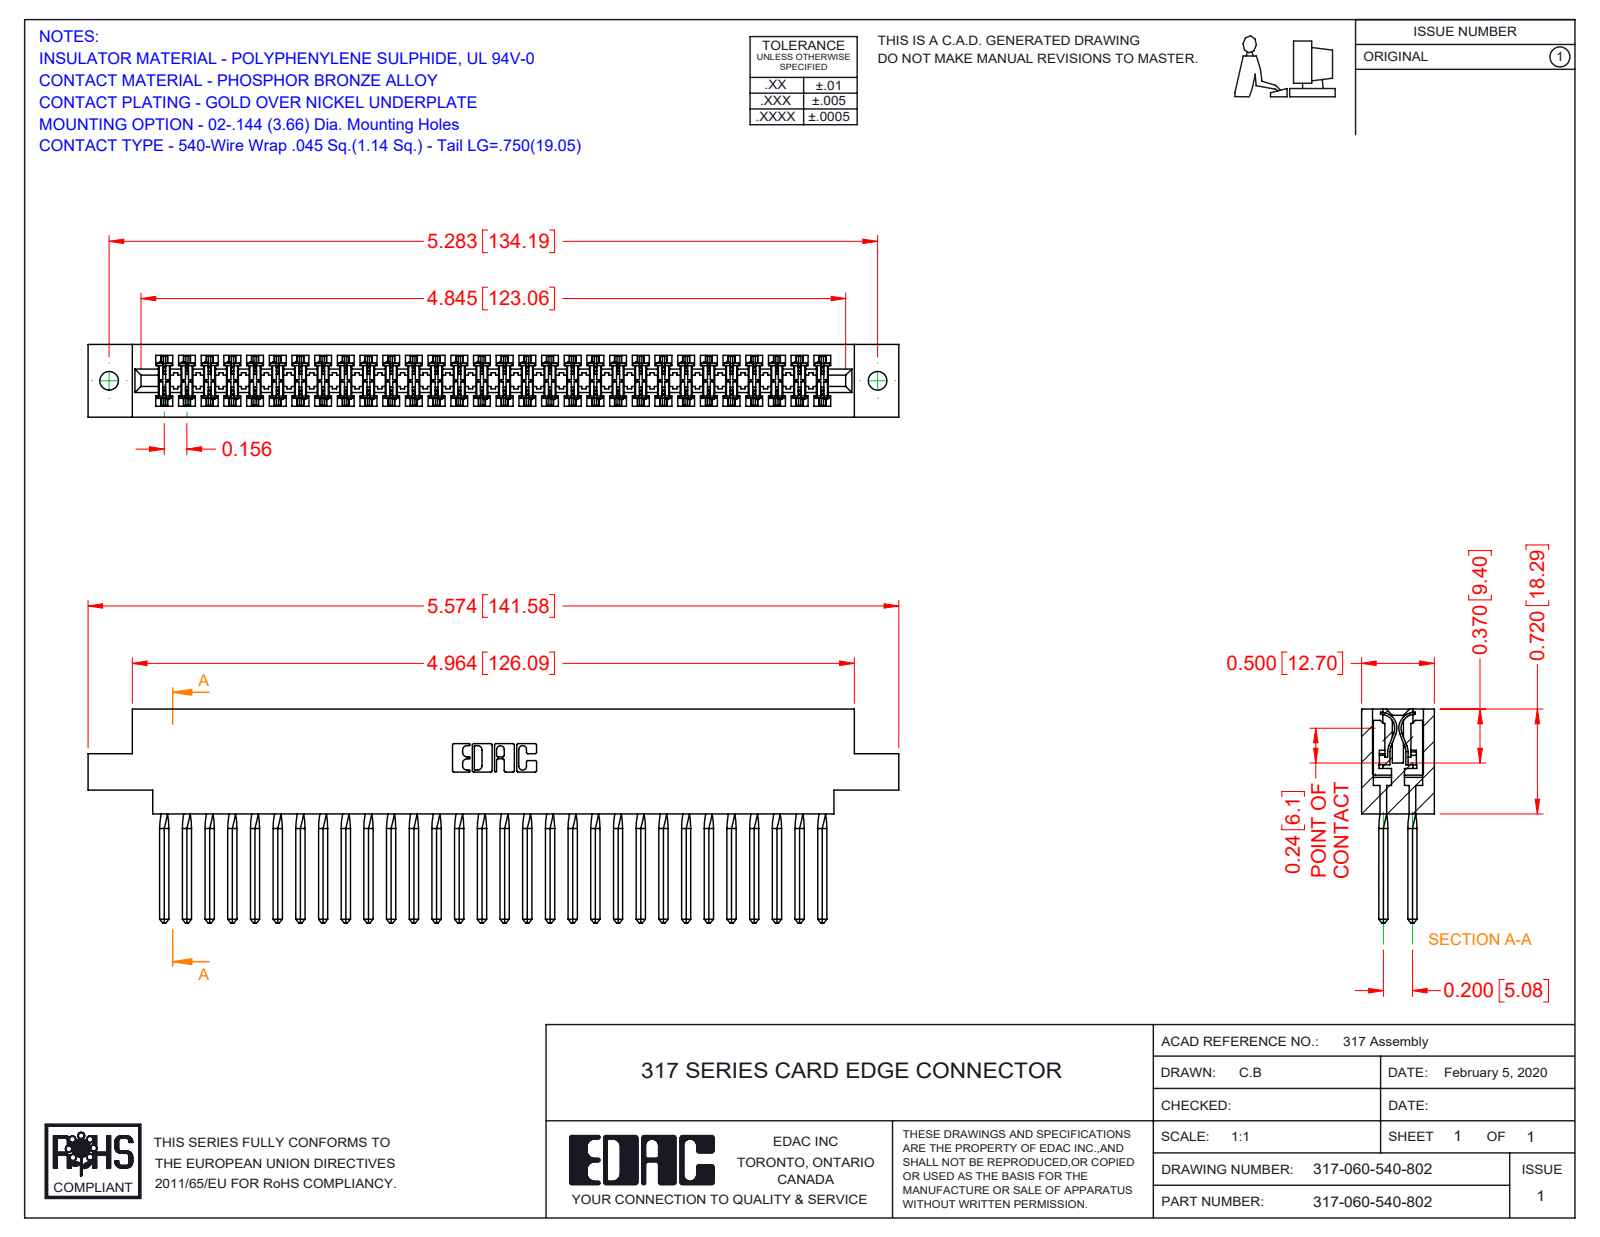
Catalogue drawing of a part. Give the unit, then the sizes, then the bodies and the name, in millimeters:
Units: millimetres
Overall size (bounding box): 141.6 × 37.3 × 12.7
Round holes (diameter × count): ⌀3.3 ×2
Partial cylindrical surfaces — rounded edges, fillets, slot ends (radius × count): R0.4 ×120, R0.3 ×22, R0.2 ×6, R0.8 ×6, R0.7 ×3, R2.4 ×2, R2.5 ×2, R2.8 ×2
Main face-to-face distances: 12.7, 1.9, 10.8, 8.9, 2.8, 5, 2.4, 5.1, 18.3, 2.9
Hole centre spacings: 134.2
Volume: 23 320 mm³ · Surface area: 34 050 mm²
Bodies: 61 solids, 5442 faces (4438 planar, 764 cylindrical, 240 other)
Part name (STEP PRODUCT): 317 Part_.144 Dia; 317-290-001_540; 317-060-540-802
STEP written by: SolidWorks 2016 (CONFIG_CONTROL_DESIGN)
